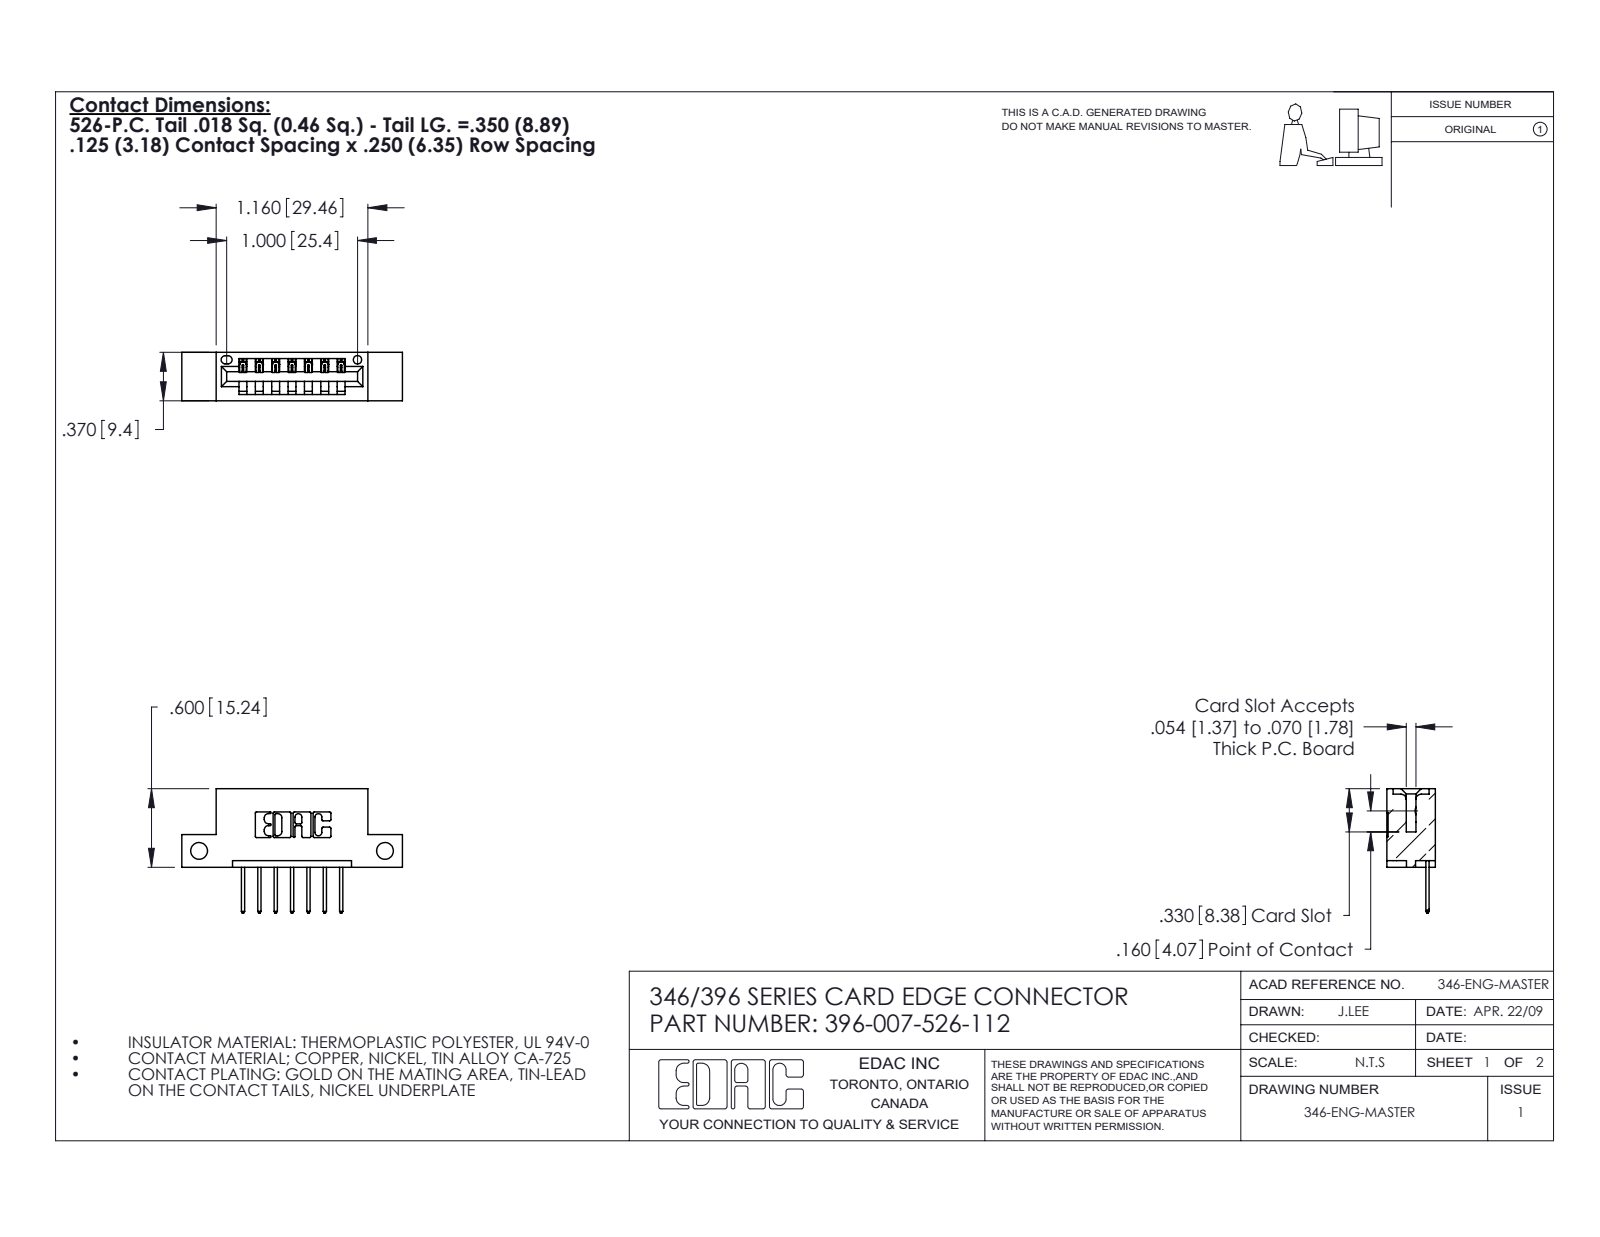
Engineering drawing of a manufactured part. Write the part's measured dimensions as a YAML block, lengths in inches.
part_name: "346 Part_Flush Mounting Lugs - Side Mount; 396-007-526-112; 345-292-001_345-293-126"
step_written_by: "SolidWorks 2020 (CONFIG_CONTROL_DESIGN)"
units: inches
bodies: {solids: 8, faces: 528, planar: 356, cylindrical: 172, other: 0}
overall_size: [1.685, 0.95, 0.37]
volume: 0.23
surface_area: 6.468
round_holes:
  - {diameter: 0.128, count: 2}
  - {diameter: 0.064, count: 1}
partial_cylinders:
  - {radius: 0.01, count: 22}
  - {radius: 0.006, count: 14}
  - {radius: 0.01, count: 14}
  - {radius: 0.007, count: 6}
  - {radius: 0.031, count: 6}
  - {radius: 0.026, count: 3}
  - {radius: 0.031, count: 2}
  - {radius: 0.04, count: 2}
face_to_face_distances: [0.25, 0.37, 0.048, 0.322, 0.148, 0.222, 0.1, 0.174, 0.072, 0.298]
hole_center_spacings: [1.42]
